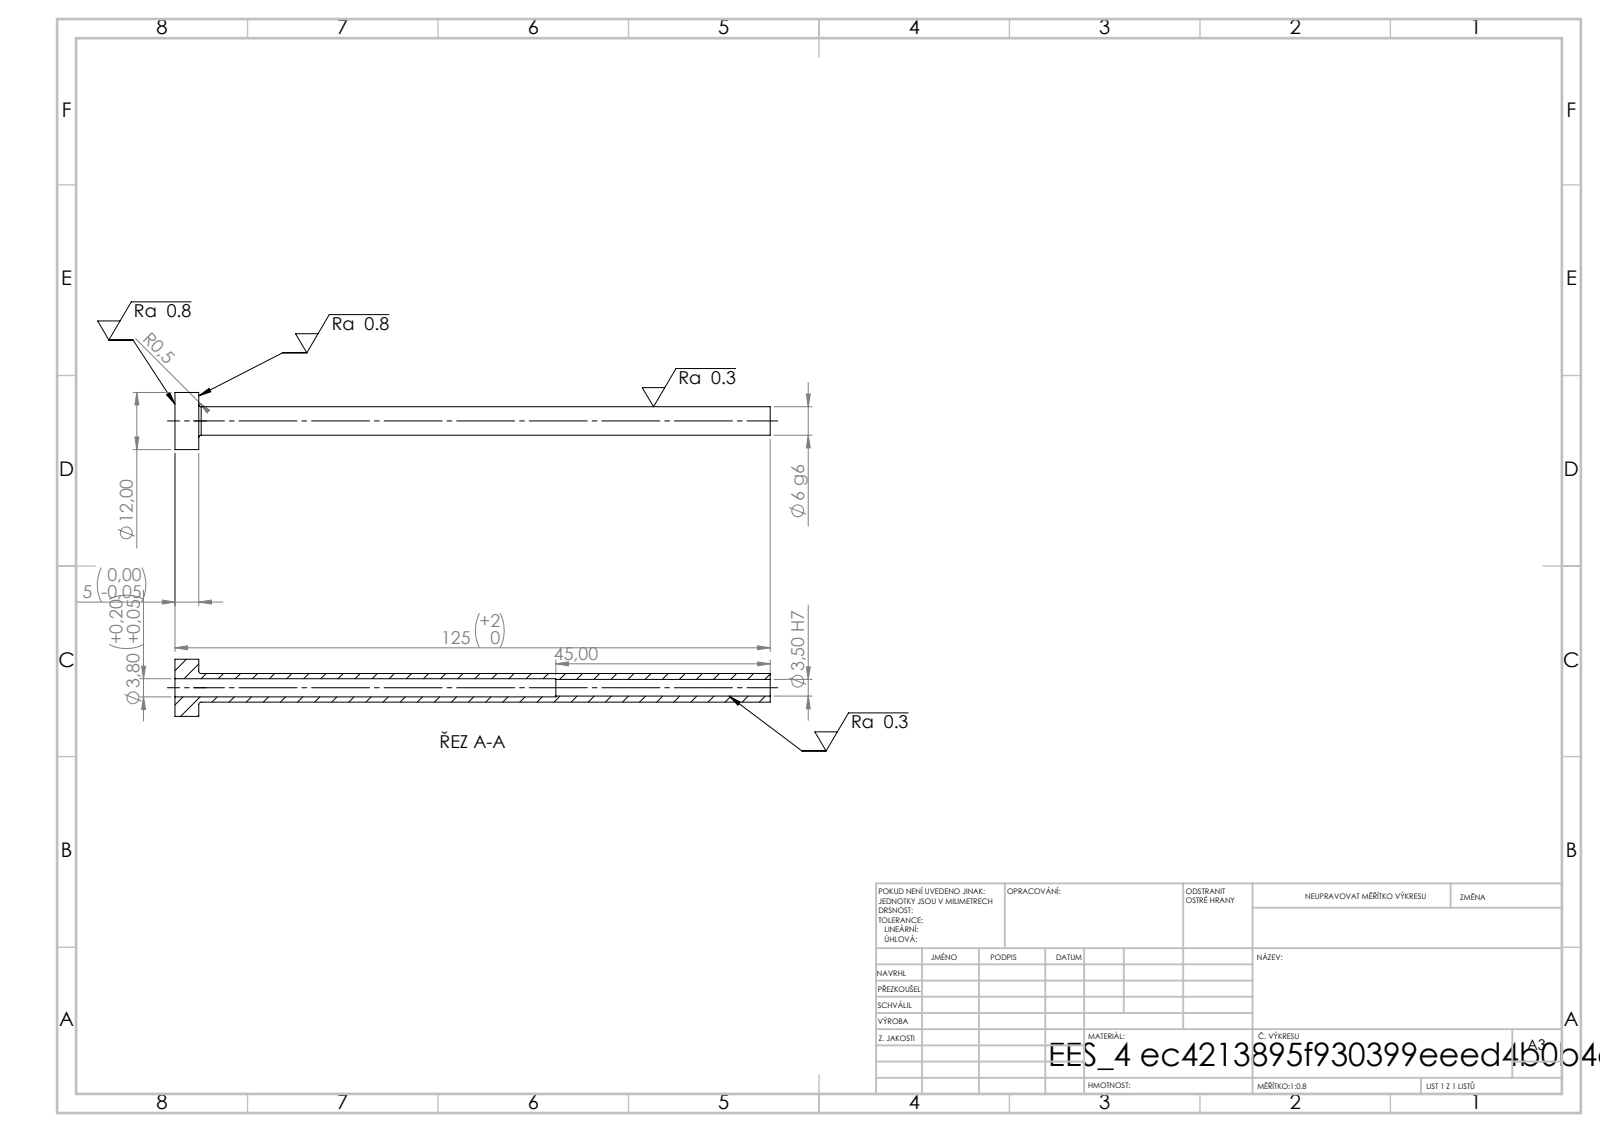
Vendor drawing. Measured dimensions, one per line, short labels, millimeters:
written by: SolidWorks 2019 (CONFIG_CONTROL_DESIGN)
unit: mm
bodies: 1 solid, 14 faces (4 planar, 8 cylindrical, 2 other)
size: 125 × 12 × 12
volume: 2 619 mm³; area: 4 103 mm²
holes: 1× ⌀3.5, 1× ⌀3.8
bosses: 1× ⌀12, 1× ⌀6
face distances: 5, 125, 120, 80, 75, 45
